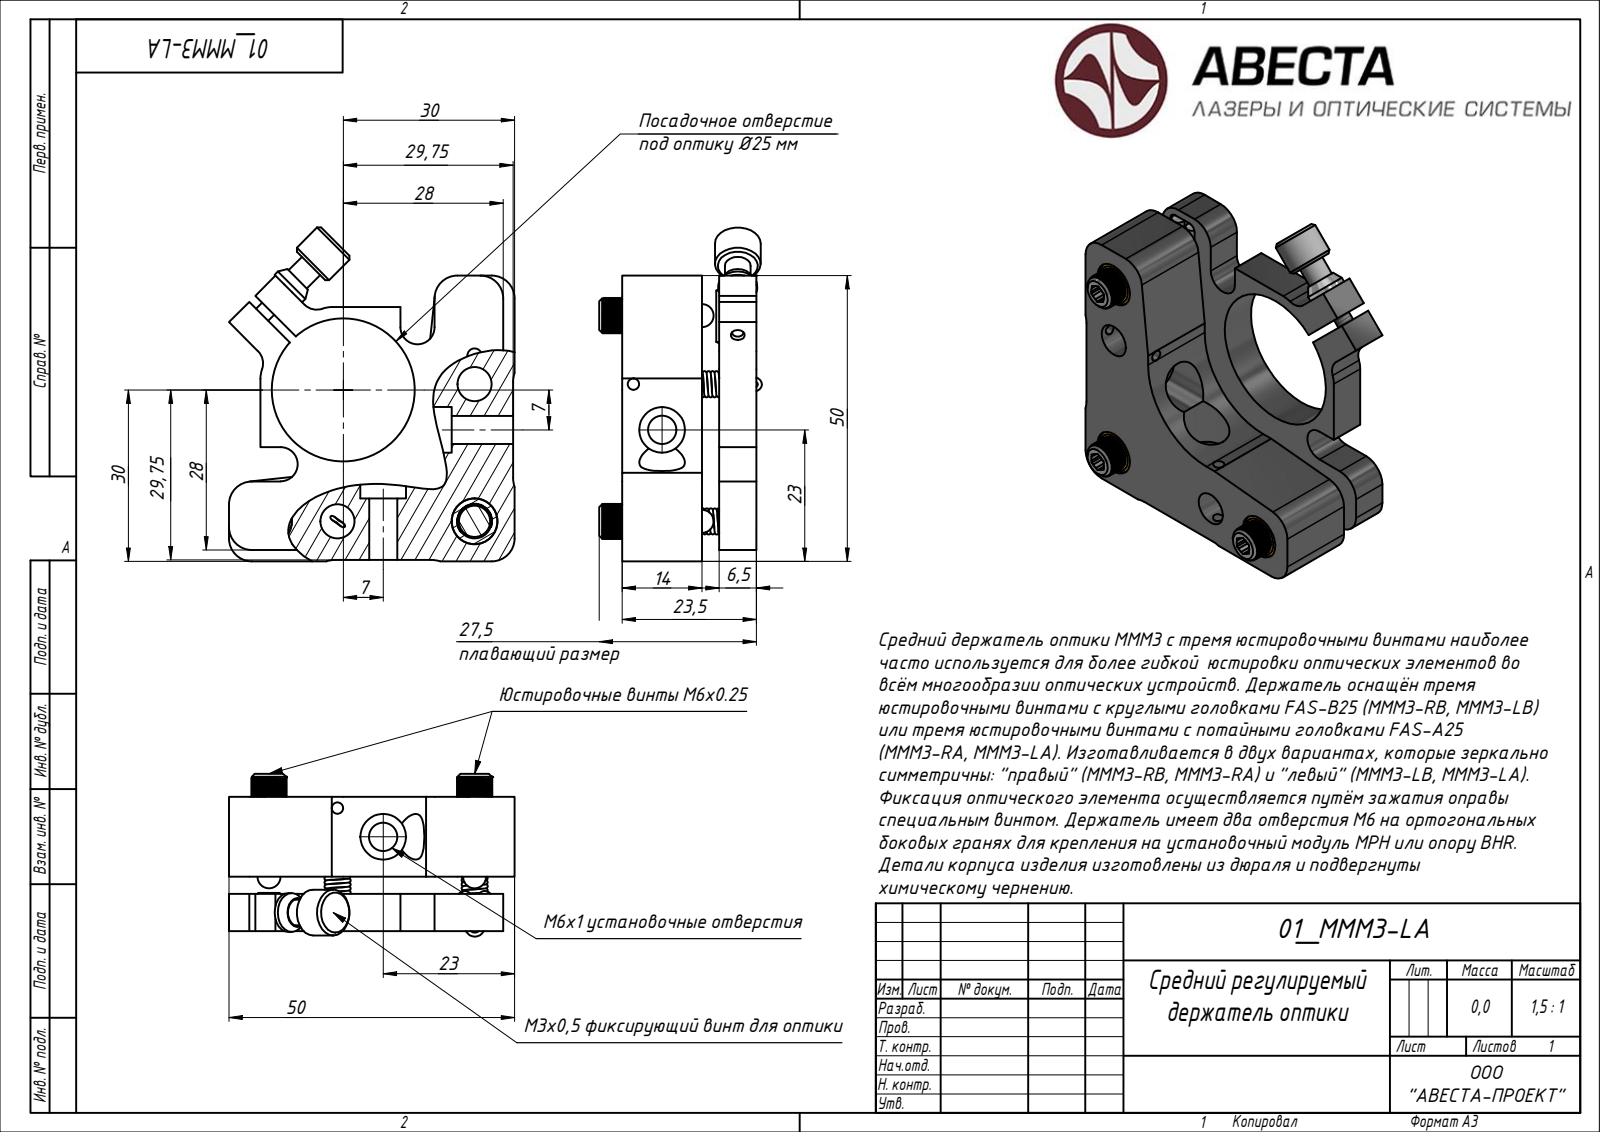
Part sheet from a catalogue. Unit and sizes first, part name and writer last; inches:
Units: inches
Overall size (bounding box): 2.3 × 1.969 × 1.632
Main face-to-face distances: 0.256, 0.157, 0.551, 0.709, 0.965, 0.413, 0.079, 0.069, 0.217, 1.969
Volume: 1.64 in³ · Surface area: 26.81 in²
Bodies: 15 solids, 347 faces (144 planar, 0 cylindrical, 203 other)
STEP written by: ST-DEVELOPER v15 (AUTOMOTIVE_DESIGN)
